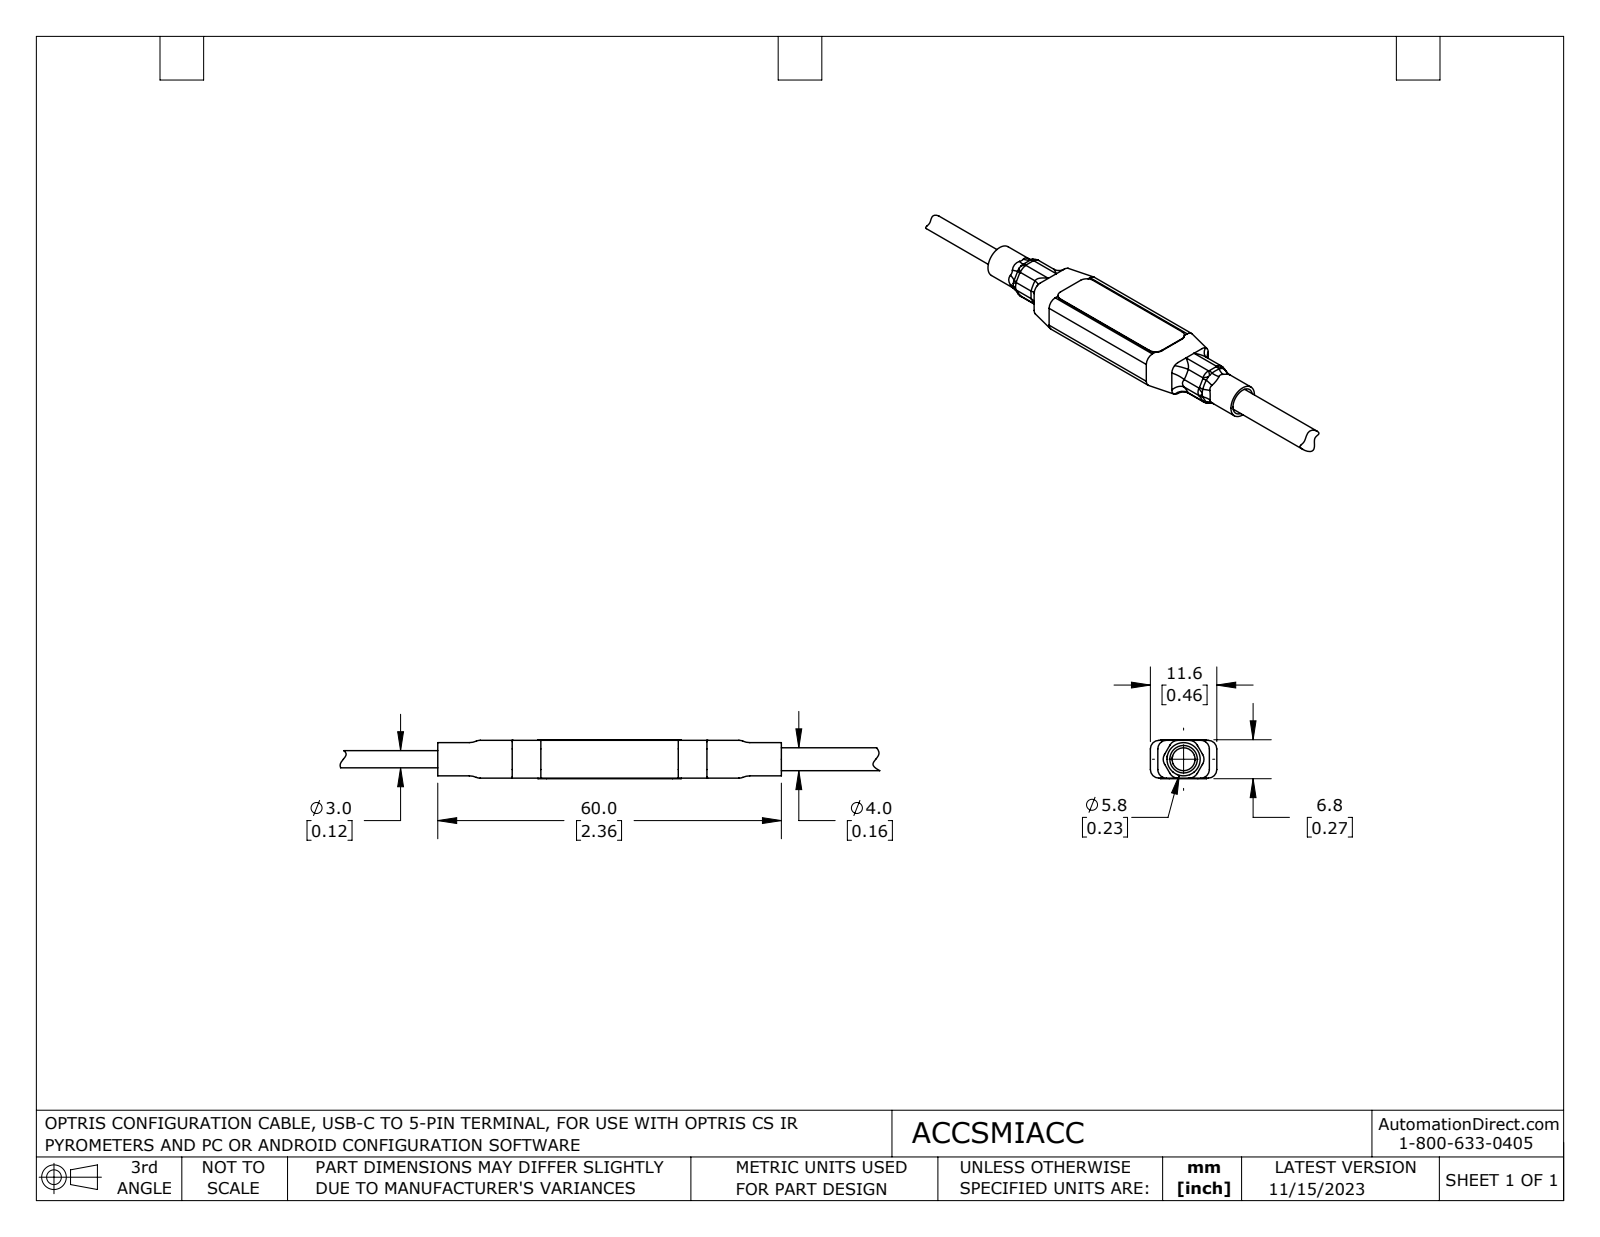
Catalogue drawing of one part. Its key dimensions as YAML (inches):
part_name: "ACCSMIACC"
step_written_by: "SolidWorks 2021 (AUTOMOTIVE_DESIGN)"
units: inches
bodies: {solids: 9, faces: 825, planar: 277, cylindrical: 310, other: 238}
overall_size: [3.71, 0.457, 0.268]
volume: 0.128
surface_area: 12.06
round_holes:
  - {diameter: 0.118, count: 2}
  - {diameter: 0.079, count: 1}
  - {diameter: 0.181, count: 1}
  - {diameter: 0.189, count: 1}
round_bosses_or_shafts:
  - {diameter: 0.031, count: 10}
  - {diameter: 0.035, count: 8}
  - {diameter: 0.02, count: 4}
  - {diameter: 0.228, count: 1}
  - {diameter: 0.205, count: 1}
  - {diameter: 0.197, count: 1}
  - {diameter: 0.157, count: 1}
partial_cylinders:
  - {radius: 0.02, count: 56}
  - {radius: 0.012, count: 48}
  - {radius: 0.008, count: 24}
  - {radius: 0.039, count: 16}
  - {radius: 0.059, count: 12}
  - {radius: 0.043, count: 6}
  - {radius: 0.063, count: 6}
  - {radius: 0.031, count: 4}
face_to_face_distances: [0.02, 0.024, 0.24, 0.22, 0.217, 0.197, 0.043, 0.26, 0.244, 0.264]
